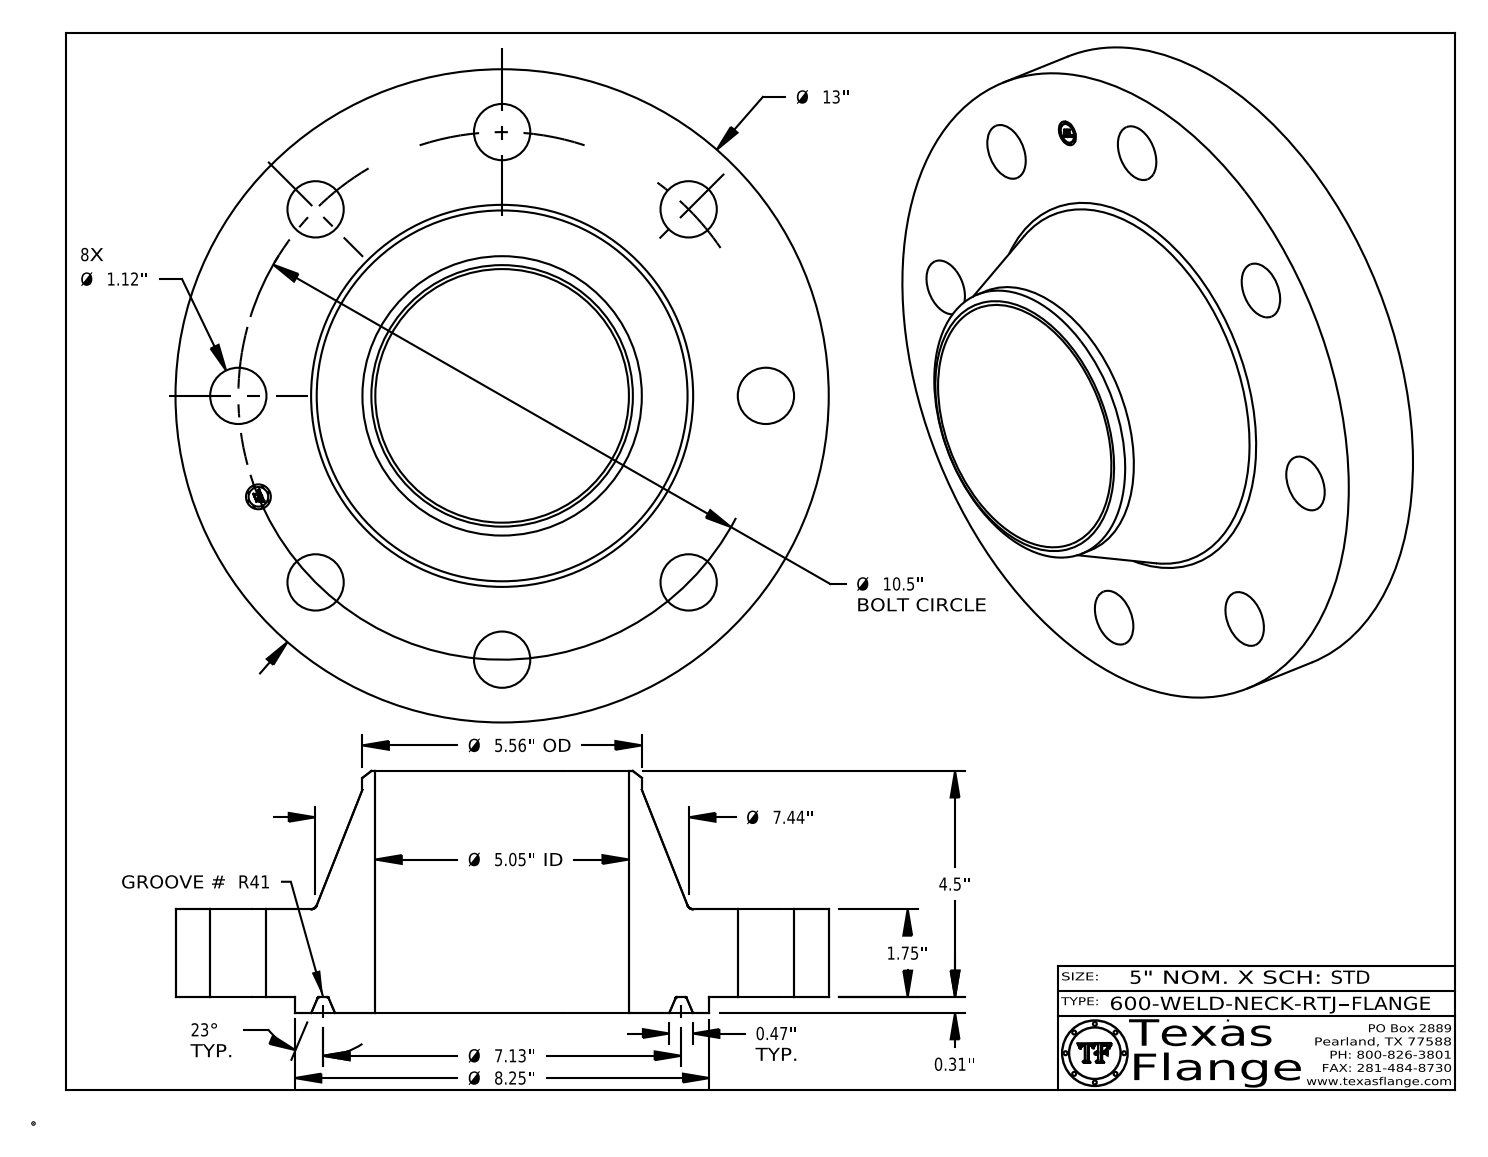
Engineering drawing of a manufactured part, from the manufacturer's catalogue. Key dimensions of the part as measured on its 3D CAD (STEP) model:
Part name (STEP PRODUCT): 600-WELD-NECK-RTJ
STEP written by: CATIA V5 STEP AP214 (AUTOMOTIVE_DESIGN)
Units: inches
Bodies: 1 solid, 429 faces (371 planar, 44 cylindrical, 14 other)
Overall size (bounding box): 13 × 13 × 4.813
Volume: 224.9 in³ · Surface area: 461.5 in²
Round holes (diameter × count): ⌀1.12 ×8, ⌀0.495 ×1, ⌀5.047 ×1
Round bosses / shafts (diameter × count): ⌀0.03 ×8, ⌀13 ×1, ⌀8.25 ×1, ⌀5.56 ×1, ⌀0.39 ×1
Main face-to-face distances: 1.75, 0.313, 2.063, 4.813, 4.5, 2.75, 2.048, 1.735, 0.015, 2.765
Hole centre spacings: 5.25, 4.018, 9.701, 7.424, 7.425, 2.048, 5.833, 8.73
